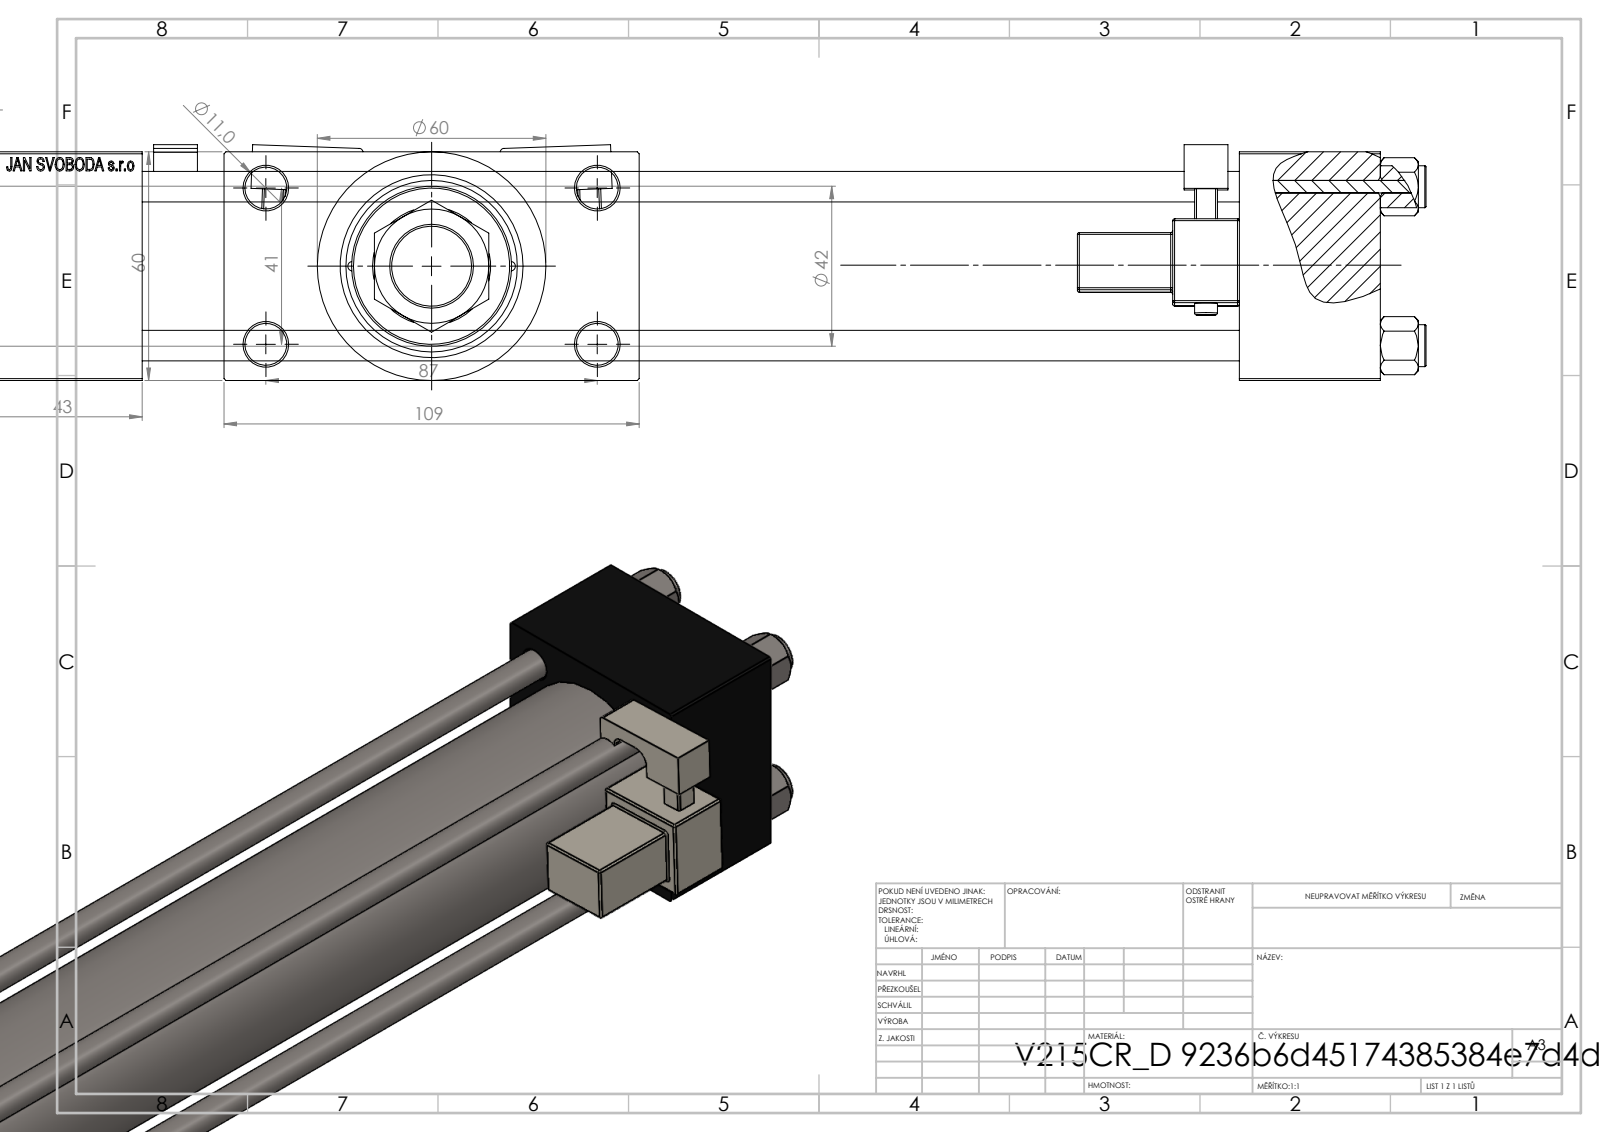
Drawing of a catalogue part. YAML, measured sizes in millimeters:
part_name: "NUT_M5_D; V215_VC_A; V215CR_MSU; V215CR_D_TYCINKA (+3 more)"
step_written_by: "SolidWorks 2019 (CONFIG_CONTROL_DESIGN)"
units: millimeters
bodies: {solids: 14, faces: 1320, planar: 576, cylindrical: 156, other: 588}
overall_size: [460, 109, 61.9]
volume: 875214
surface_area: 252247
round_holes:
  - {diameter: 8, count: 4}
  - {diameter: 11, count: 4}
  - {diameter: 2.5, count: 2}
  - {diameter: 7, count: 2}
  - {diameter: 16.66, count: 2}
  - {diameter: 24, count: 2}
  - {diameter: 18.5, count: 1}
  - {diameter: 28, count: 1}
  - {diameter: 31, count: 1}
  - {diameter: 40, count: 1}
  - {diameter: 45, count: 1}
round_bosses_or_shafts:
  - {diameter: 11, count: 4}
  - {diameter: 6, count: 2}
  - {diameter: 60, count: 1}
  - {diameter: 46, count: 1}
  - {diameter: 42, count: 1}
  - {diameter: 22, count: 1}
  - {diameter: 14, count: 1}
partial_cylinders:
  - {radius: 0.5, count: 48}
  - {radius: 1, count: 2}
  - {radius: 2.5, count: 2}
  - {radius: 4, count: 2}
  - {radius: 13.5, count: 1}
face_to_face_distances: [60, 288, 24.5, 84.5, 37, 325, 368, 331, 43, 109]
hole_center_spacings: [20.85, 22.65, 29.49, 30.62, 41.7, 46.53, 47.15, 48.09]
